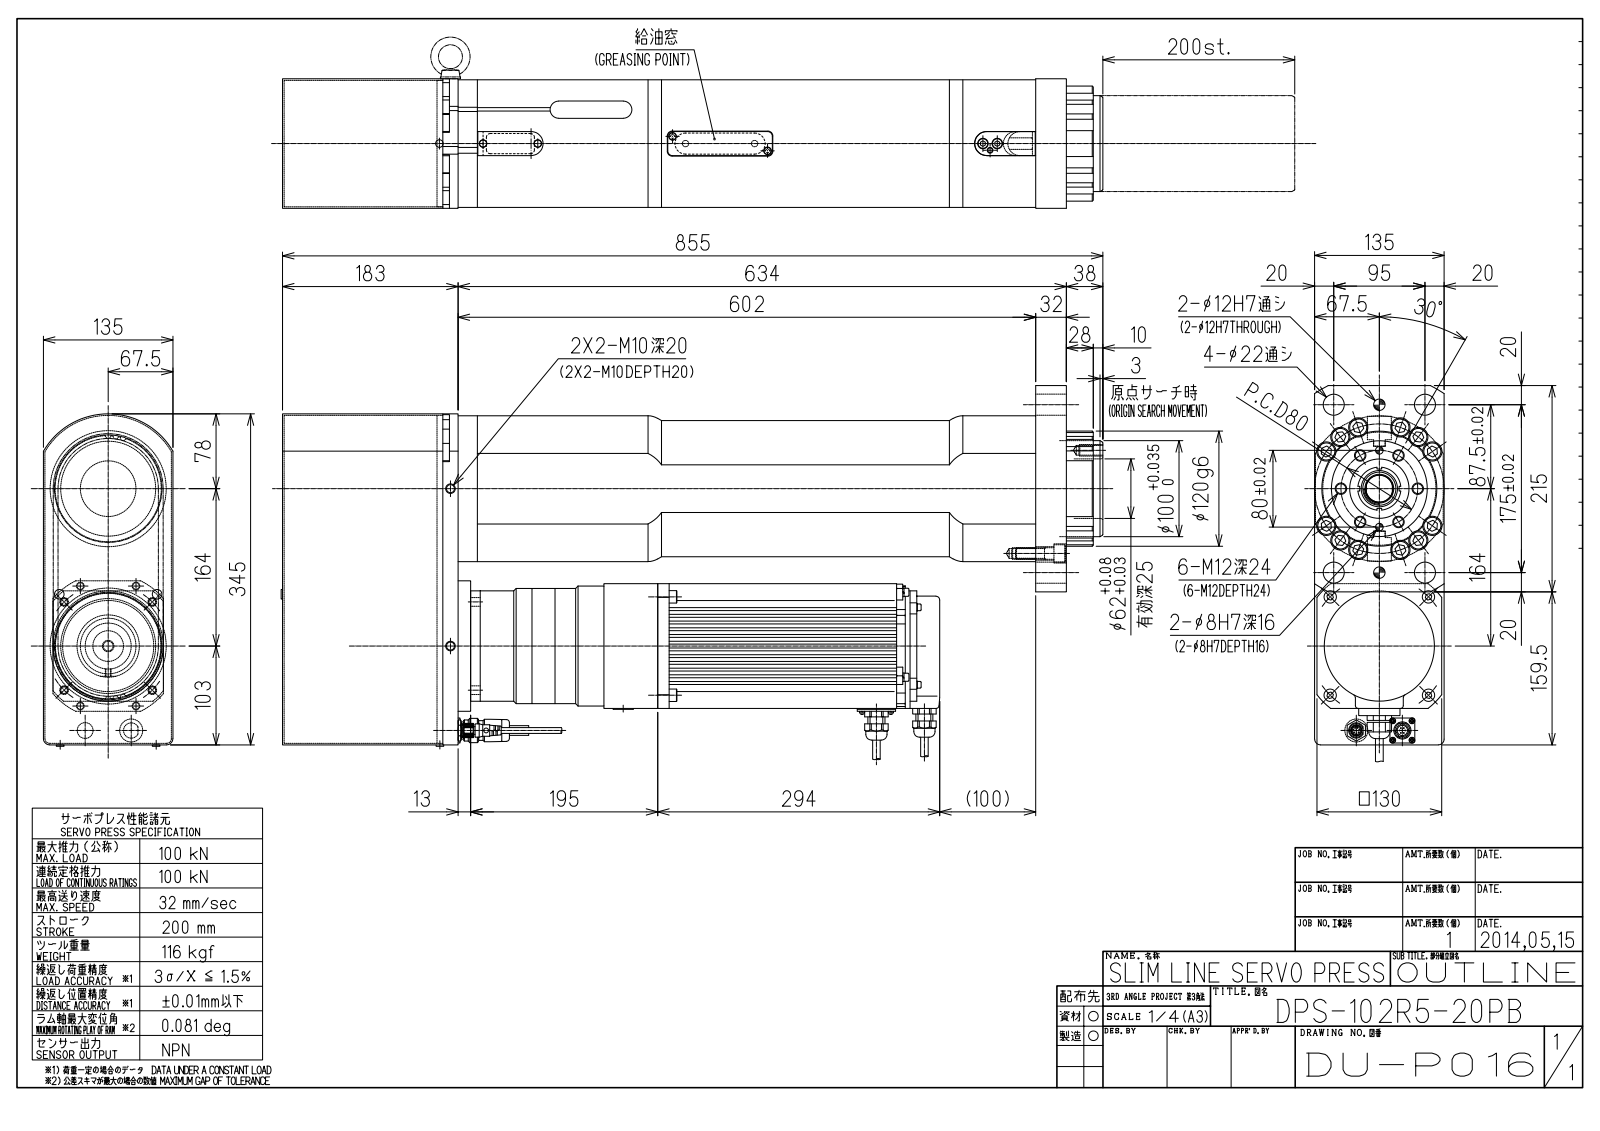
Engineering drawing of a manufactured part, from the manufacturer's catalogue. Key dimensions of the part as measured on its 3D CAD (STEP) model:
Part name (STEP PRODUCT): DPS-102R5-20PB_Shrinkwrap_1; DS-P001-02_OUTLINE; DPS-102R5-20PB_OUTLINE
STEP written by: Autodesk Inventor 2015 (AUTOMOTIVE_DESIGN)
Units: millimetres
Bodies: 3 solids, 1238 faces (699 planar, 385 cylindrical, 154 other)
Overall size (bounding box): 859.4 × 388.51 × 135
Volume: 25 950 000 mm³ · Surface area: 1 380 000 mm²
Round holes (diameter × count): ⌀6.65 ×12, ⌀3.24 ×11, ⌀10.11 ×6, ⌀4.5 ×4, ⌀4.92 ×4, ⌀8 ×4, ⌀9 ×4, ⌀9.1 ×4, ⌀11 ×4, ⌀22 ×4, ⌀2.46 ×3, ⌀6.6 ×2
Round bosses / shafts (diameter × count): ⌀18 ×9, ⌀6 ×5, ⌀8.5 ×4, ⌀4 ×4, ⌀120 ×2, ⌀10 ×2, ⌀142 ×1, ⌀125 ×1
Partial cylindrical surfaces — rounded edges, fillets, slot ends (radius × count): R5 ×49, R2 ×26, R1 ×10, R4 ×9, R0.5 ×8, R10 ×7, R2.5 ×6, R3 ×5
Main face-to-face distances: 135, 3, 6, 71, 68, 9, 65, 28, 74, 25
Hole centre spacings: 40, 97.37, 47.5, 69.28, 125.2, 7.51, 10.26, 20.71
